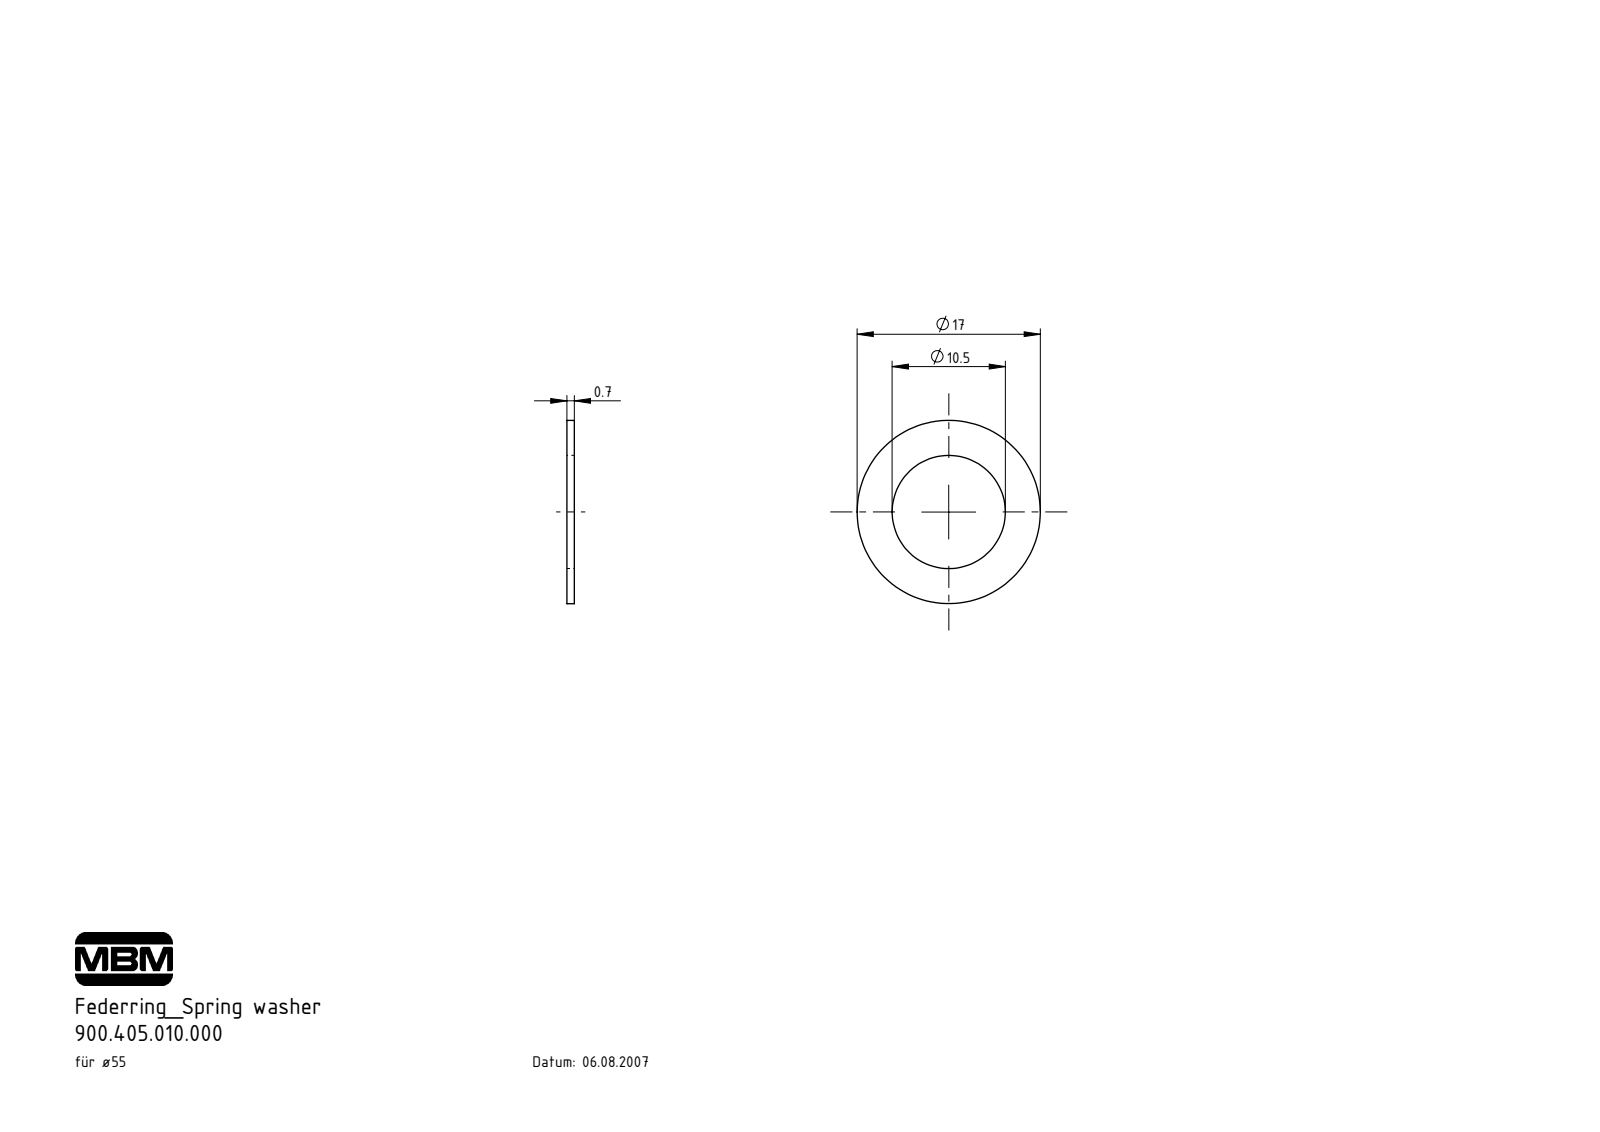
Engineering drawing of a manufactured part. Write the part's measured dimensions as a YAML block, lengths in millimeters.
part_name: "900.405.010.000"
step_written_by: "SolidWorks 2022 (AUTOMOTIVE_DESIGN)"
units: millimeters
bodies: {solids: 1, faces: 6, planar: 2, cylindrical: 4, other: 0}
overall_size: [17, 17, 0.7]
volume: 98
surface_area: 341
round_holes:
  - {diameter: 10.5, count: 1}
round_bosses_or_shafts:
  - {diameter: 17, count: 1}
face_to_face_distances: [0.7]
